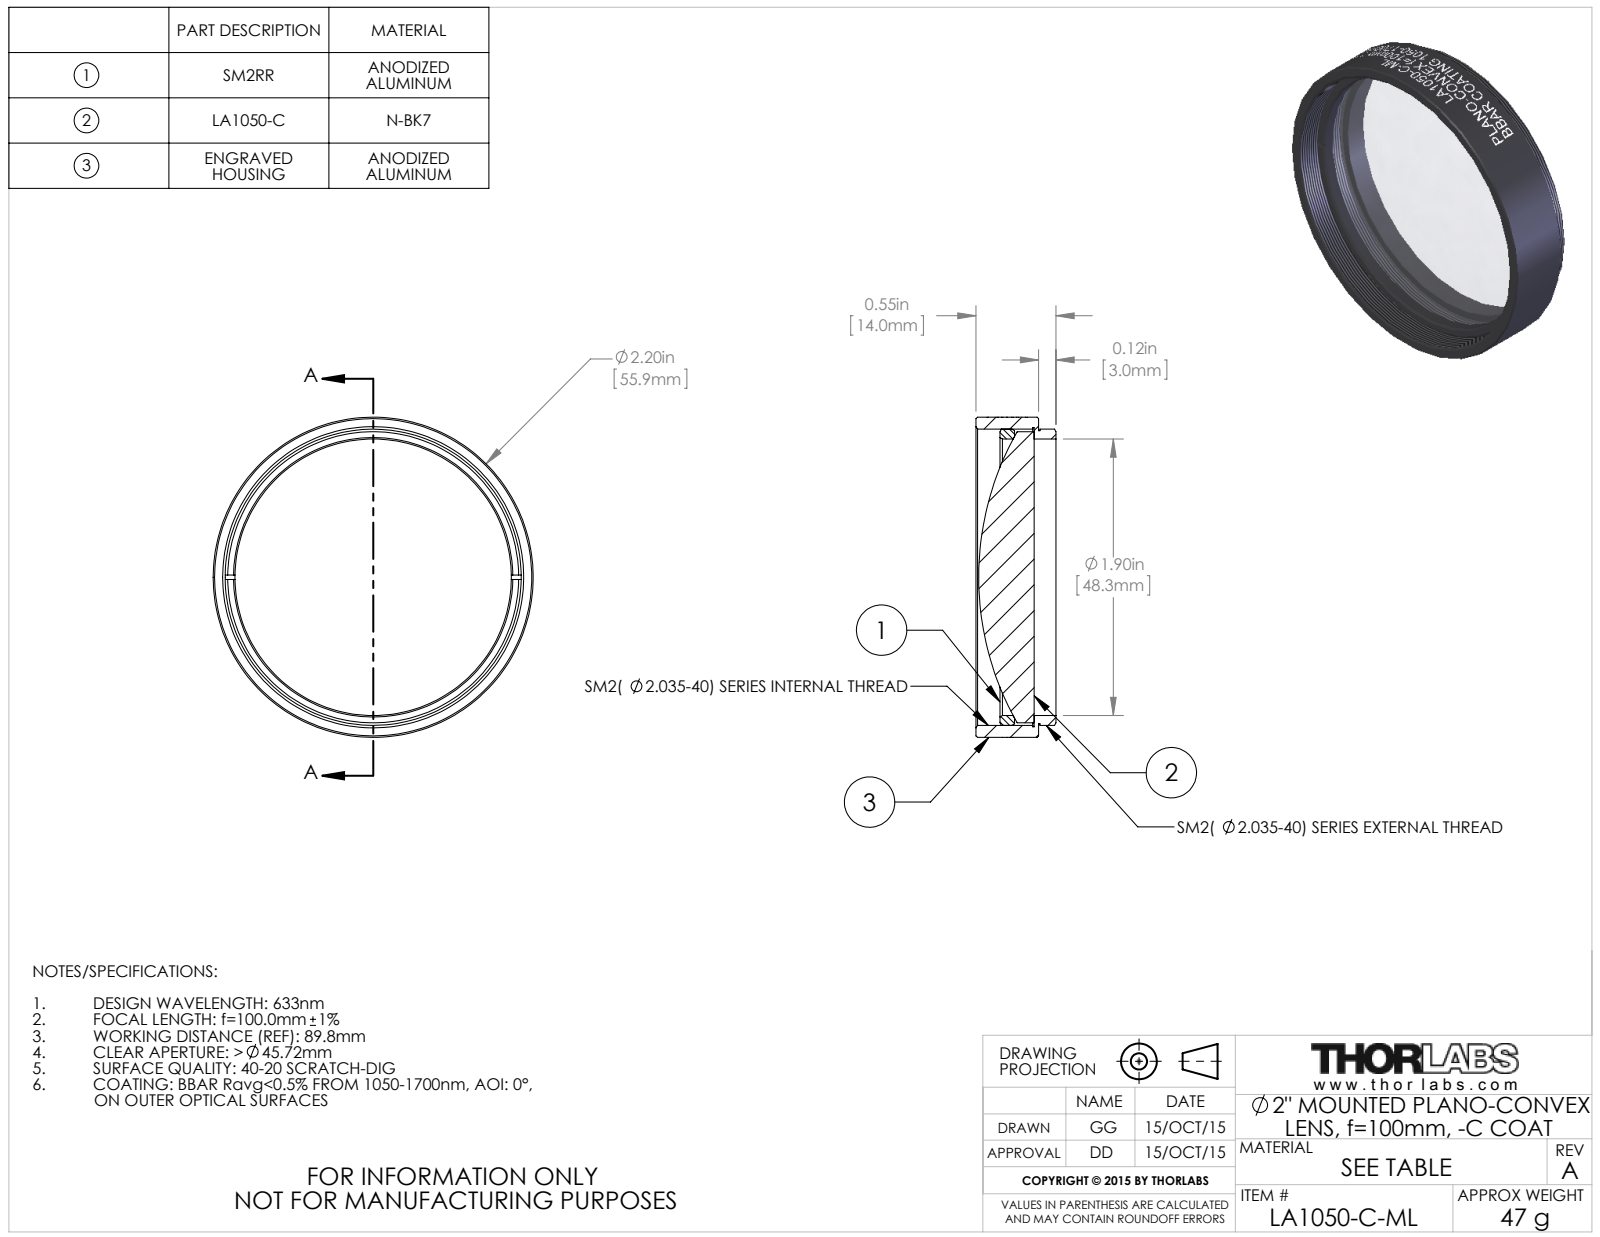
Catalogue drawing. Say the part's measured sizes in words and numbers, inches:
The part is named "TTN039500-E0W". Its 3-D file was written by "SolidWorks 2014 (CONFIG_CONTROL_DESIGN)". It is 3 solids with 149 faces: 16 planar, 109 cylindrical and 24 other. Overall it measures 2.2 by 2.2 by 0.55 inches. Its volume is 1.129 cubic inches and its surface area 18.33 square inches. Round holes: 1 of diameter 1.9, 1 of diameter 2.055. Round bosses or shafts: 1 of diameter 2.2, 1 of diameter 2.035, 1 of diameter 2.015, 1 of diameter 2. The main face-to-face distances are 0.03, 0.43, 0.4, 0.12, 0.15, 0.55, 0.286, 0.166, 0.136, 0.264.
